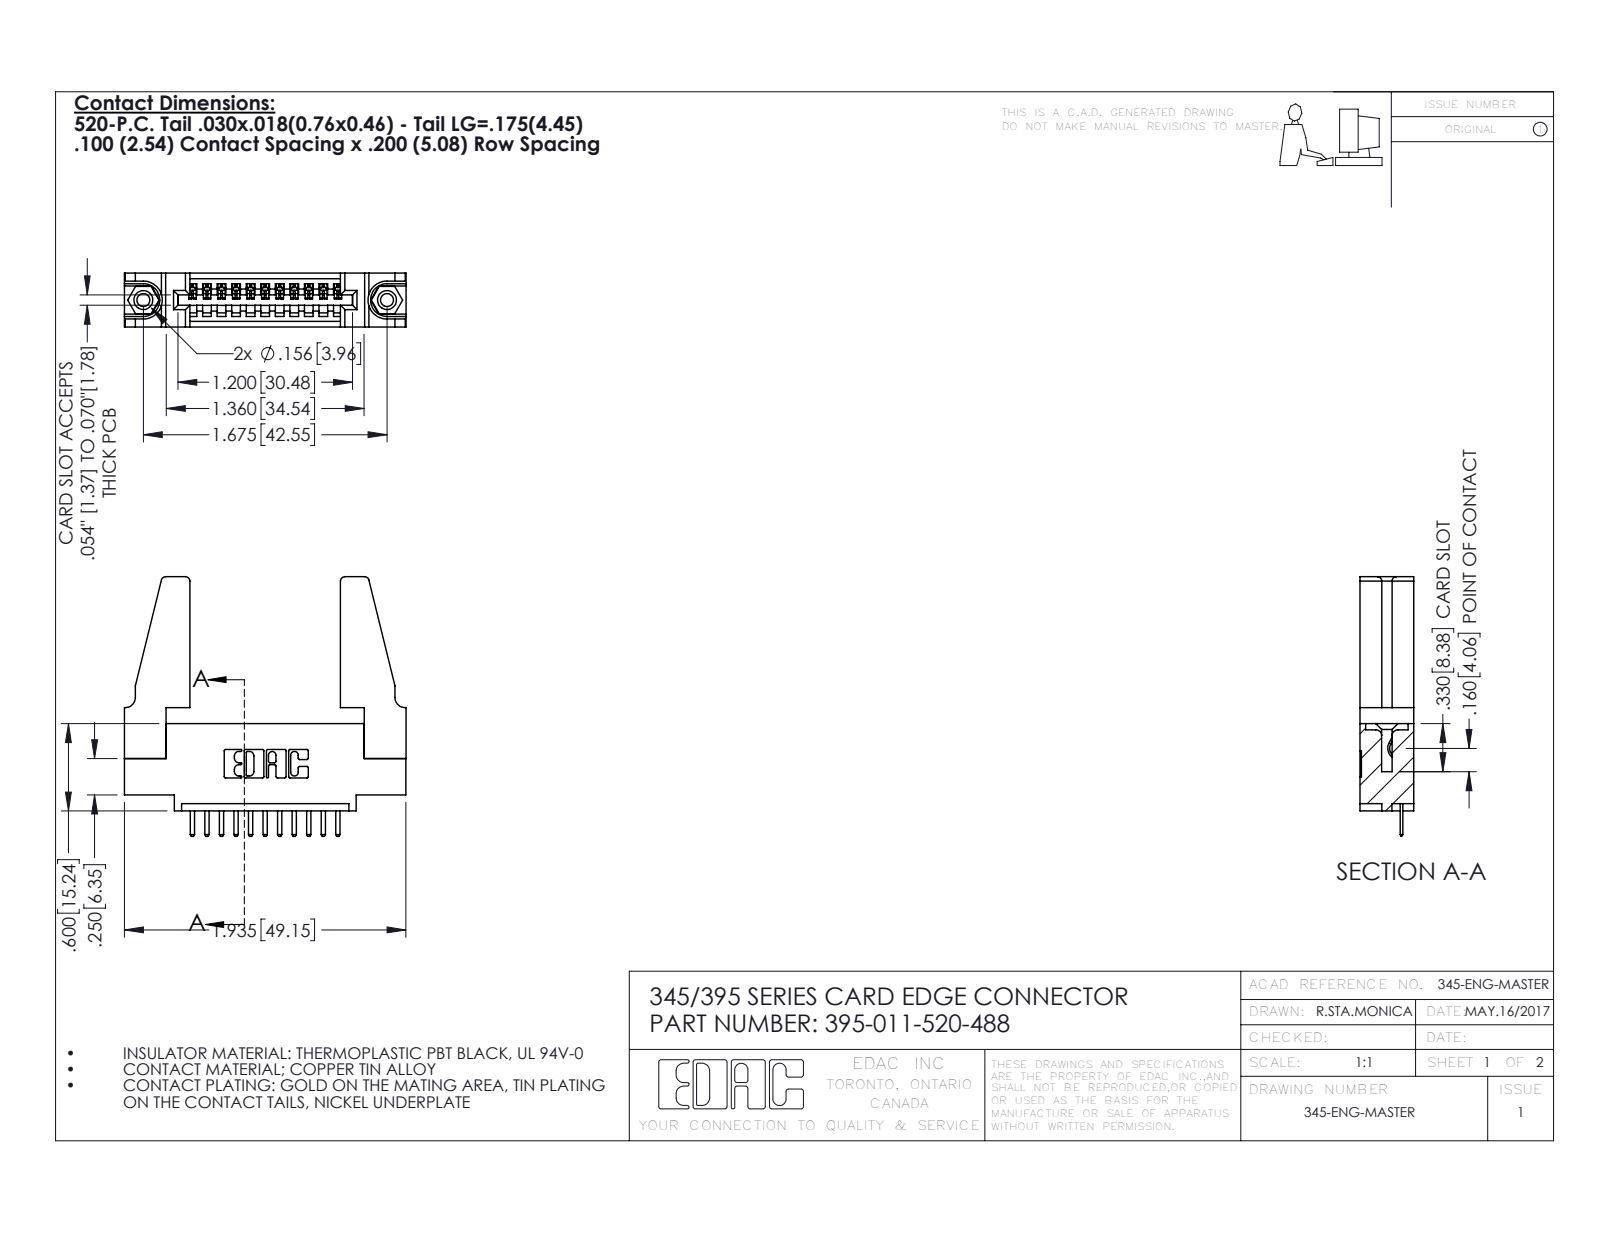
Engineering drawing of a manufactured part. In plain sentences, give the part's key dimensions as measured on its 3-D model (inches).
The part is named "345-292-001_345-293-120; 345-250-001_345-250-001-102; 395-011-520-488; 345-220-078_345-220-088 (+1 more)". Its 3-D file was written by "SolidWorks 2016 (CONFIG_CONTROL_DESIGN)". It is 16 solids with 936 faces: 618 planar, 302 cylindrical and 16 other. Overall it measures 1.936 by 1.785 by 0.37 inches. Its volume is 0.462 cubic inches and its surface area 13.05 square inches. Round holes: 2 of diameter 0.089, 2 of diameter 0.125, 2 of diameter 0.156, 1 of diameter 0.064. Round bosses or shafts: 2 of diameter 0.155. Partial cylindrical surfaces (rounded edges, fillets, slot ends): 24 of radius 0.01, 22 of radius 0.006, 22 of radius 0.01, 8 of radius 0.03, 6 of radius 0.007, 6 of radius 0.031, 3 of radius 0.026, 2 of radius 0.031. The main face-to-face distances are 0.37, 0.072, 0.298, 0.2, 0.098, 0.272, 0.025, 0.225, 0.148, 0.15. The hole center spacings are 0.27, 1.443, 1.675.
